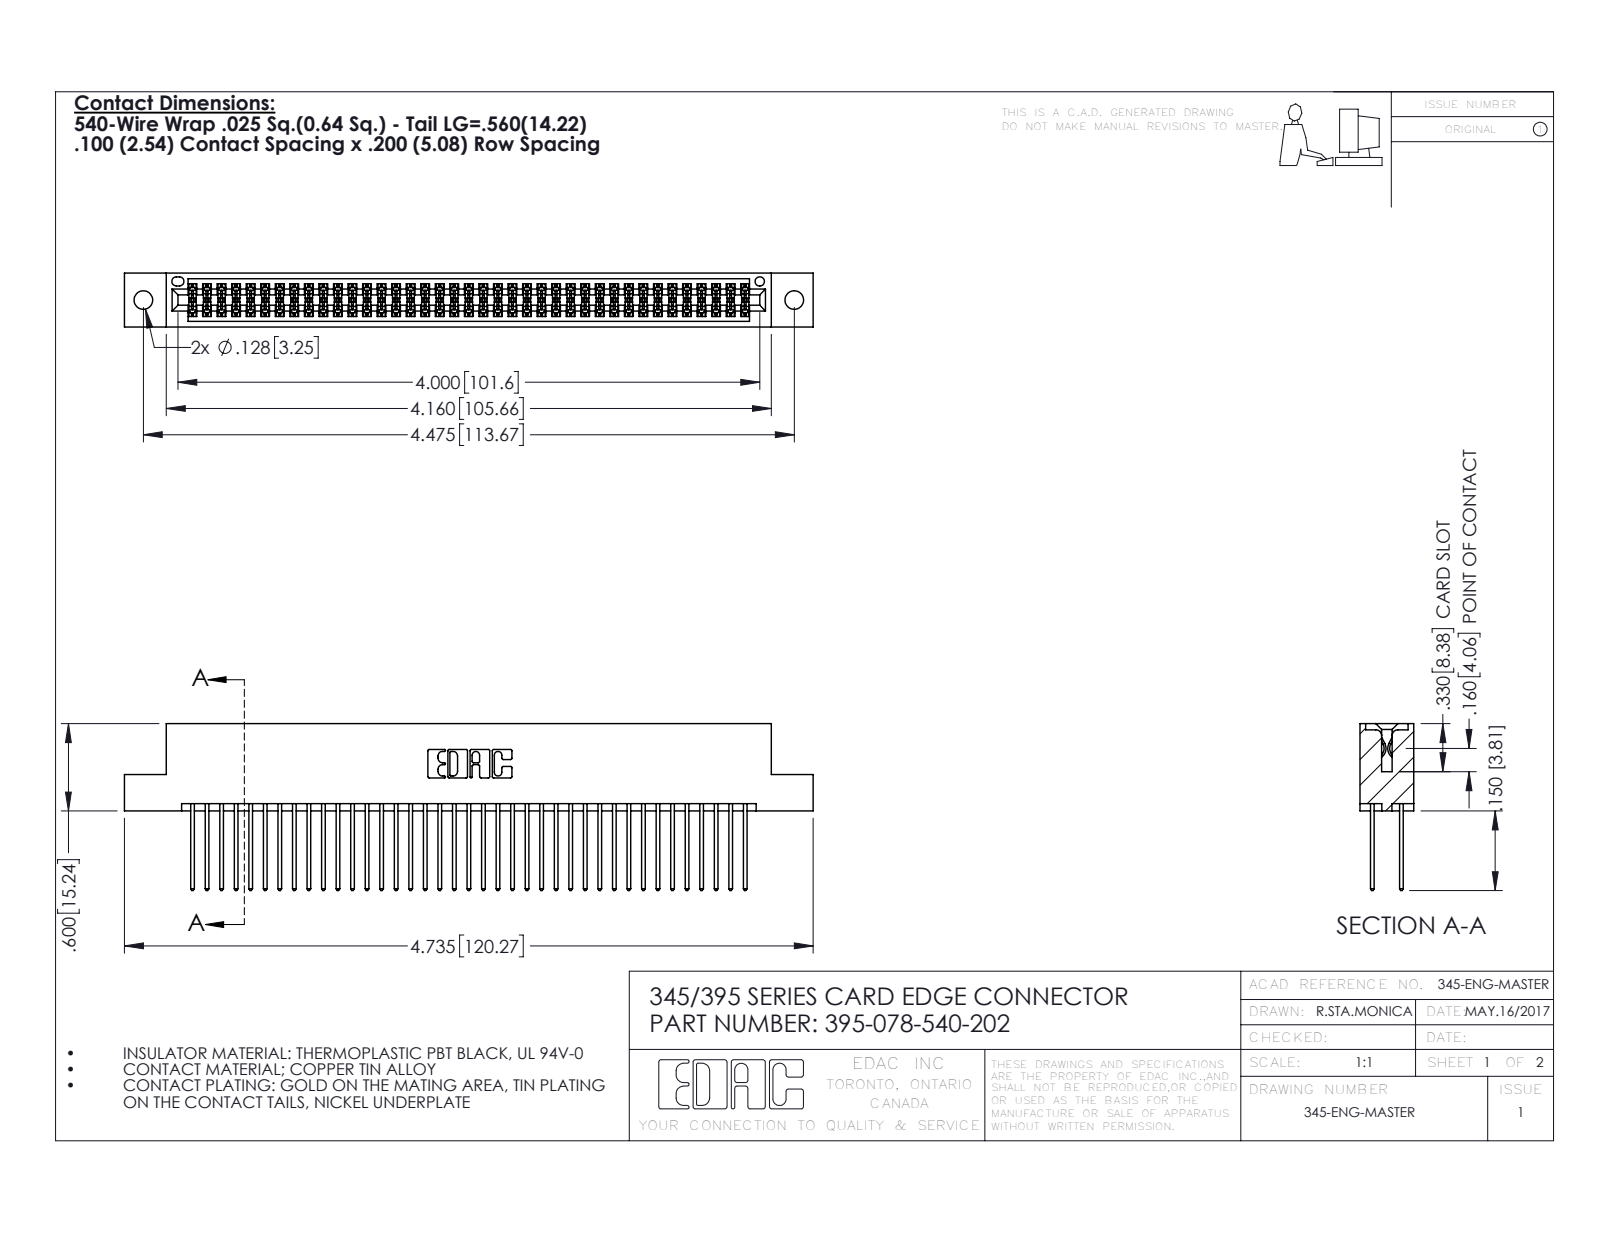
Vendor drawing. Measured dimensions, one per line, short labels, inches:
name: 345-292-001_345-293-140; 345 Part_Flush Mounting Lugs - 0.128 Dia; 395-078-540-202
written by: SolidWorks 2016 (CONFIG_CONTROL_DESIGN)
unit: in
bodies: 79 solids, 4026 faces (2654 planar, 1372 cylindrical, 0 other)
size: 4.735 × 1.147 × 0.37
volume: 0.727 in³; area: 28.91 in²
holes: 2× ⌀0.128, 1× ⌀0.064
rounds: 117× R0.006, 78× R0.01, 22× R0.01, 6× R0.007, 6× R0.031, 3× R0.026, 2× R0.014, 2× R0.019
face distances: 0.298, 0.072, 0.2, 0.098, 0.272, 0.025, 0.37, 0.225, 0.175, 0.149
hole spacings: 0.27, 4.239, 4.475
